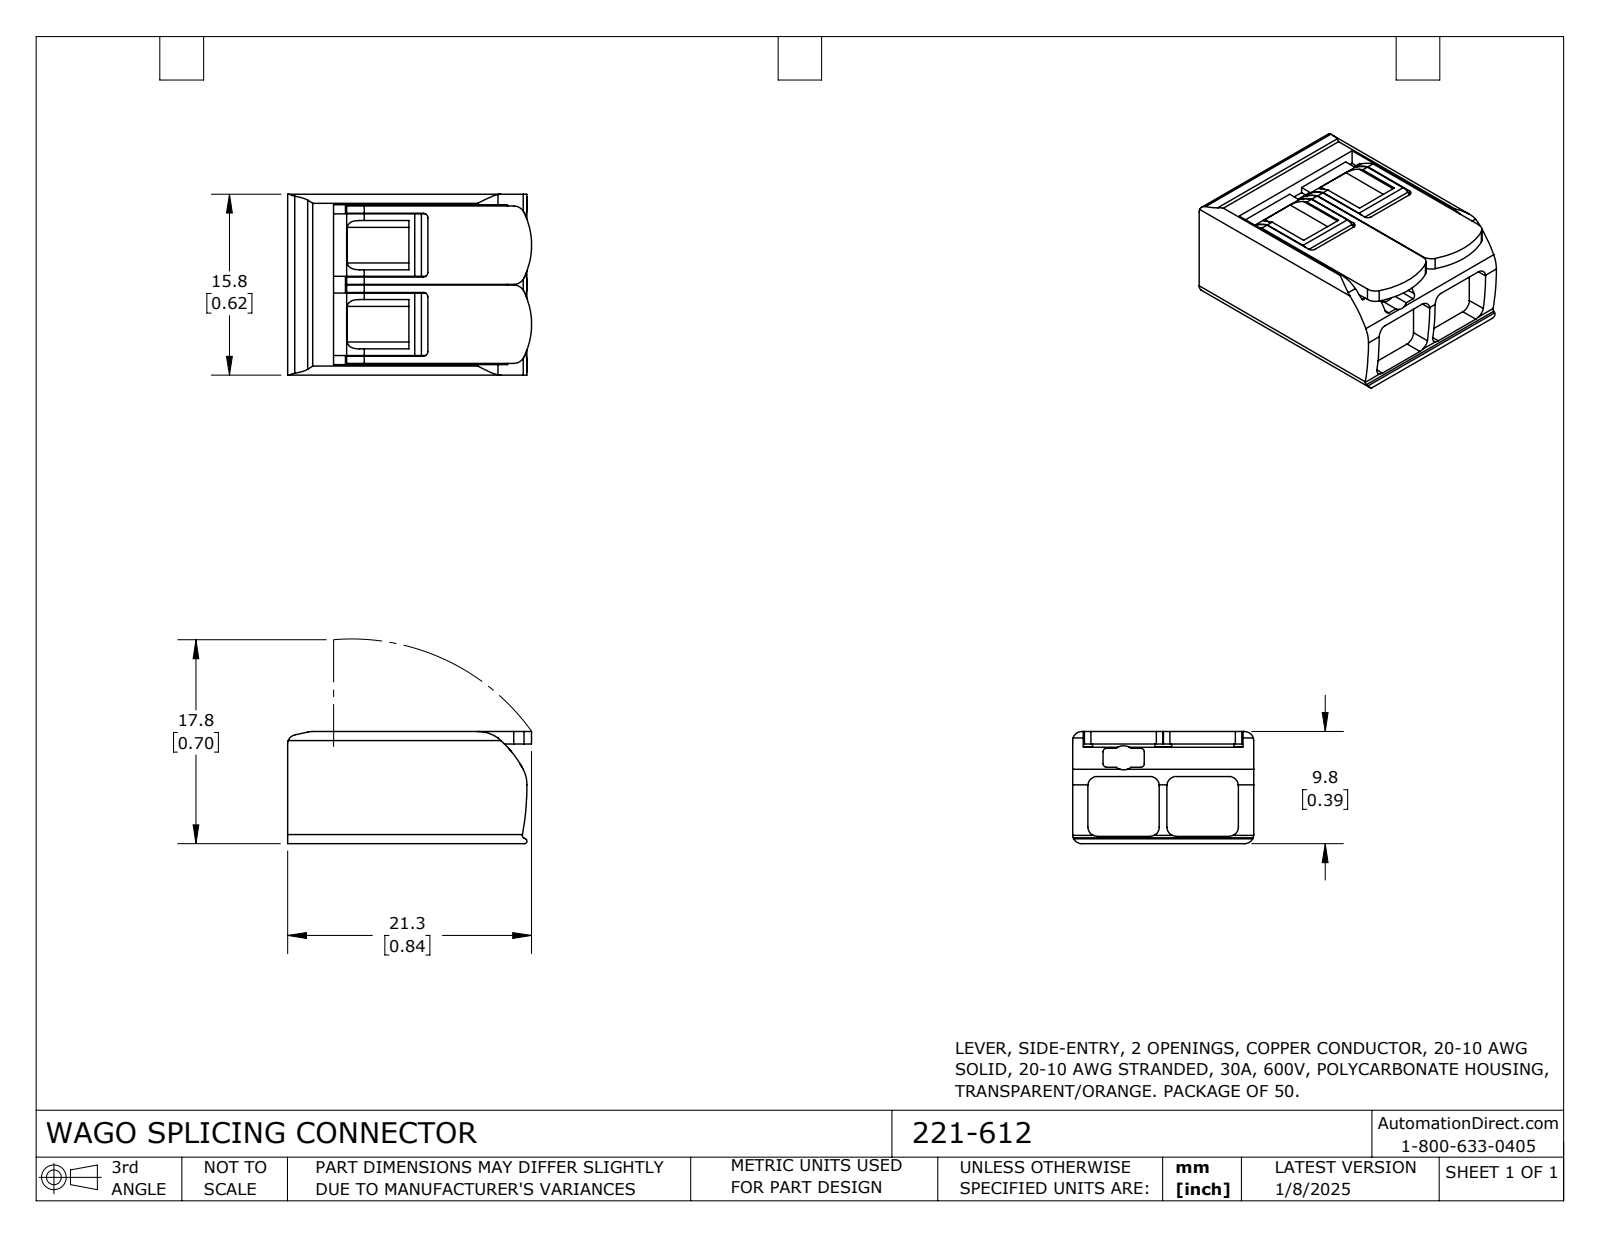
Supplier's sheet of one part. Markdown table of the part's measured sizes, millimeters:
| quantity | value |
| --- | --- |
| part name | 221-612 |
| STEP written by | SolidWorks 2023 (CONFIG_CONTROL_DESIGN) |
| units | millimeters |
| bodies | 1 solid, 125 faces (72 planar, 53 cylindrical, 0 other) |
| overall size | 21.3 × 15.8 × 9.8 |
| volume | 2 966 mm³ |
| surface area | 1 741 mm² |
| partial cylindrical surfaces (radius × count) | 0.8 × 13, 1 × 5, 0.3 × 4, 0.4 × 4, 0.6 × 4, 6.5 × 2, 0.2 × 1, 0.23 × 1 |
| main face-to-face distances | 9.8, 15.8, 18.9, 6.9, 8.7, 1.1, 0.75, 8.45, 1.35, 9.05 |
